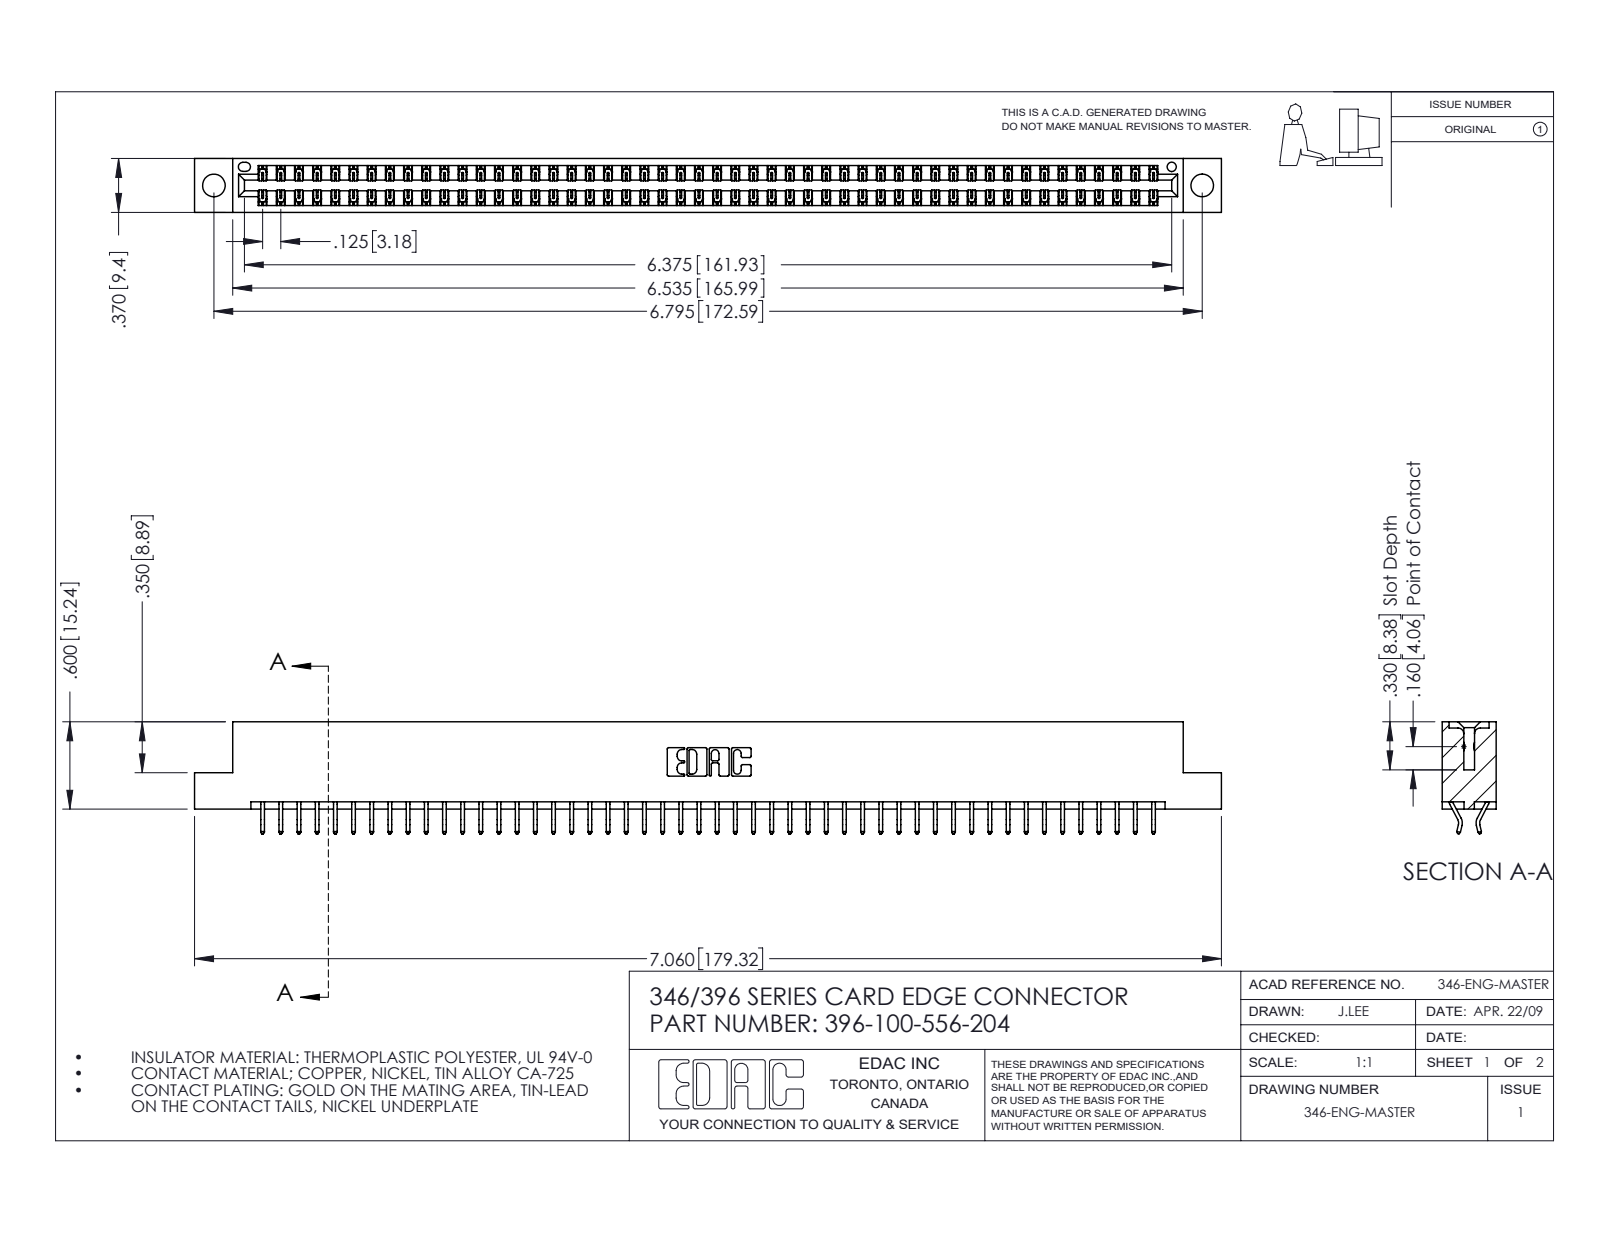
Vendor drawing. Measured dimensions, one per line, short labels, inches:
name: 396-100-556-204; 346 Part_Flush Mounting Lugs - 0.156 Dia-TH; 345-292-001_556 Tail
written by: SolidWorks 2016 (CONFIG_CONTROL_DESIGN)
unit: in
bodies: 101 solids, 5922 faces (3976 planar, 1946 cylindrical, 0 other)
size: 7.06 × 0.77 × 0.37
volume: 1.065 in³; area: 36.95 in²
holes: 2× ⌀0.156, 1× ⌀0.064
rounds: 150× R0.006, 22× R0.01, 6× R0.007, 6× R0.031, 3× R0.026, 2× R0.01, 2× R0.014, 2× R0.022
face distances: 0.048, 0.322, 0.37, 0.25, 0.025, 0.072, 0.298, 0.275, 0.148, 0.222
hole spacings: 0.246, 6.586, 6.795
